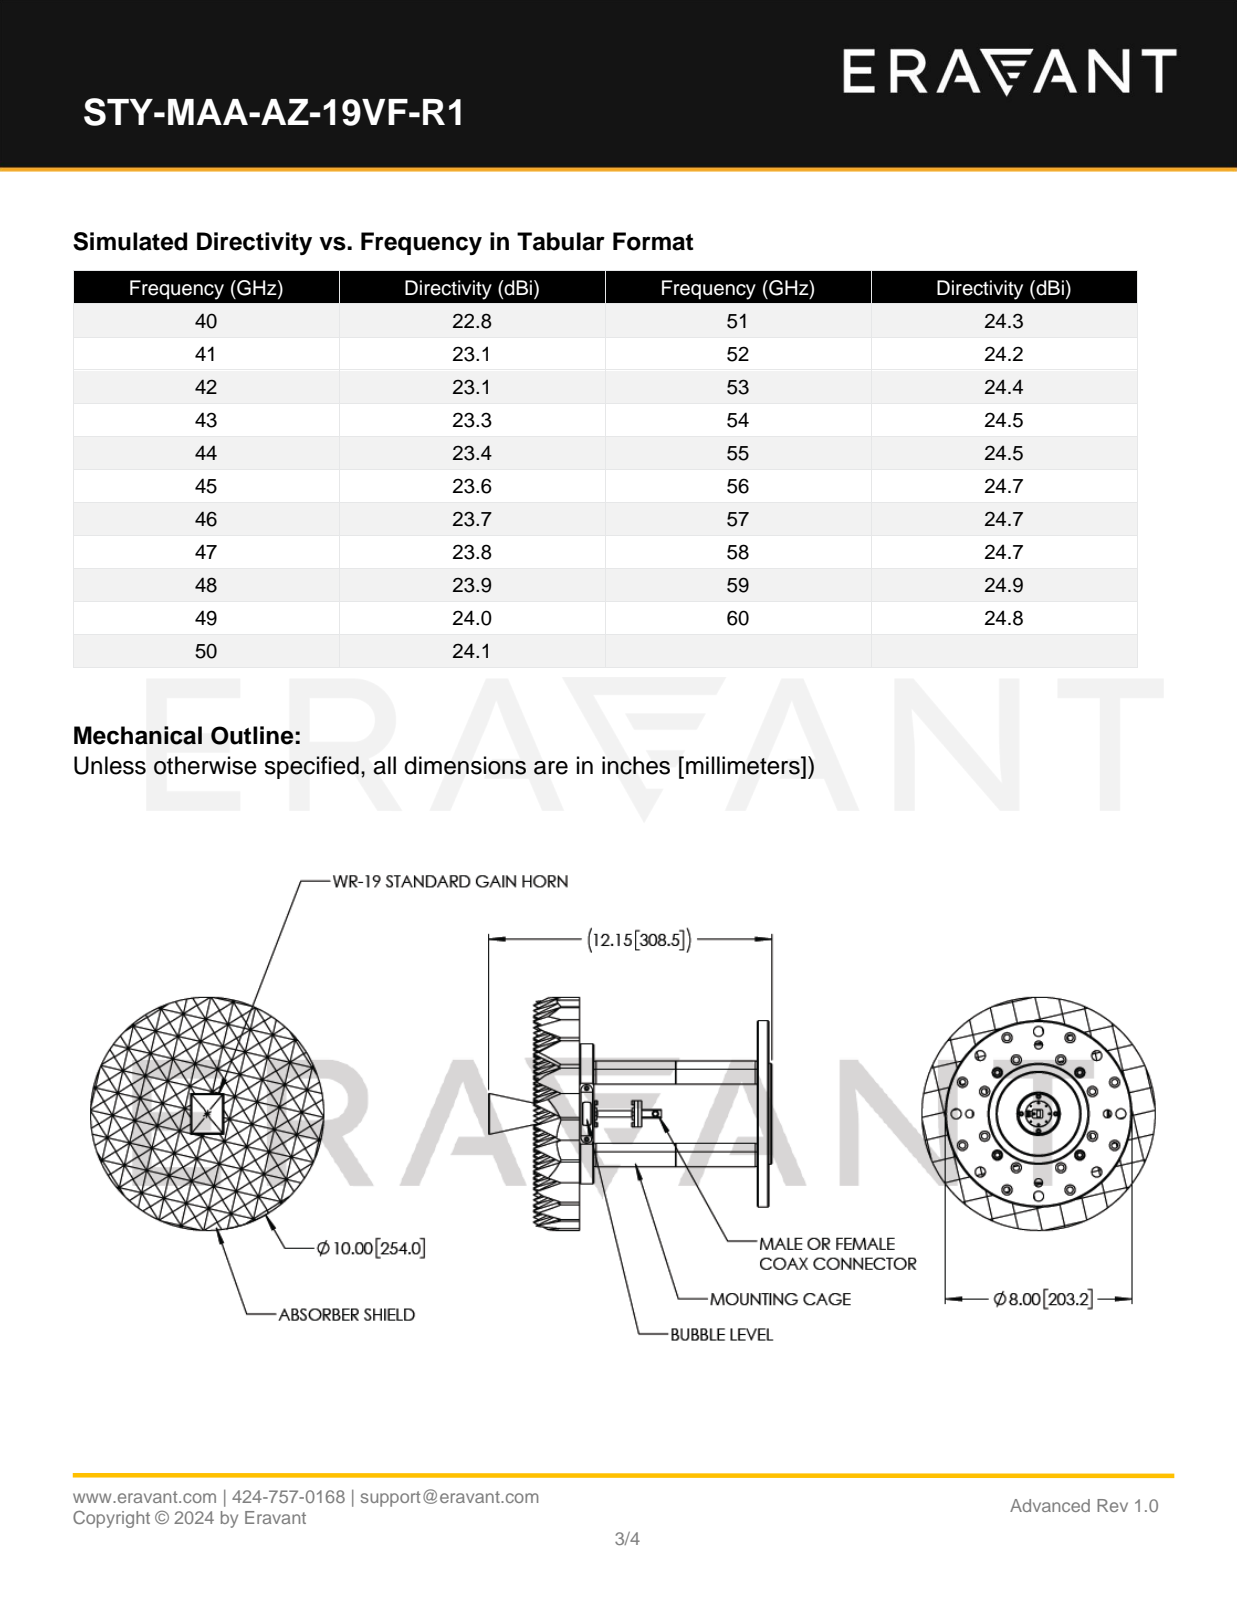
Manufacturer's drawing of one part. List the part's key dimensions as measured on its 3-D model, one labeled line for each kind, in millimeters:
Part name (STEP PRODUCT): STY-MAA-AZ-19VF-R1
STEP written by: SolidWorks 2021 (CONFIG_CONTROL_DESIGN)
Units: millimetres
Bodies: 83 solids, 1440 faces (622 planar, 343 cylindrical, 475 other)
Overall size (bounding box): 308.5 × 254 × 254
Volume: 2 533 000 mm³ · Surface area: 499 000 mm²
Round holes (diameter × count): ⌀6.8 ×20, ⌀11.1 ×16, ⌀11 ×8, ⌀8.8 ×4, ⌀19.1 ×4, ⌀2.3 ×2, ⌀3.2 ×2, ⌀4.8 ×1, ⌀45.7 ×1, ⌀90 ×1
Round bosses / shafts (diameter × count): ⌀25.4 ×4, ⌀11.1 ×4, ⌀4.6 ×4, ⌀12.7 ×2, ⌀254 ×1, ⌀203.2 ×1, ⌀152.4 ×1, ⌀110 ×1
Partial cylindrical surfaces — rounded edges, fillets, slot ends (radius × count): R0.1 ×48, R2 ×2, R6.4 ×2, R2.9 ×1, R6.1 ×1
Main face-to-face distances: 25, 50, 25, 50, 75, 100, 100, 150, 75, 125
Hole centre spacings: 109.9, 141.9, 87.8, 128.2, 150.3, 39.4, 63.4, 89.7
